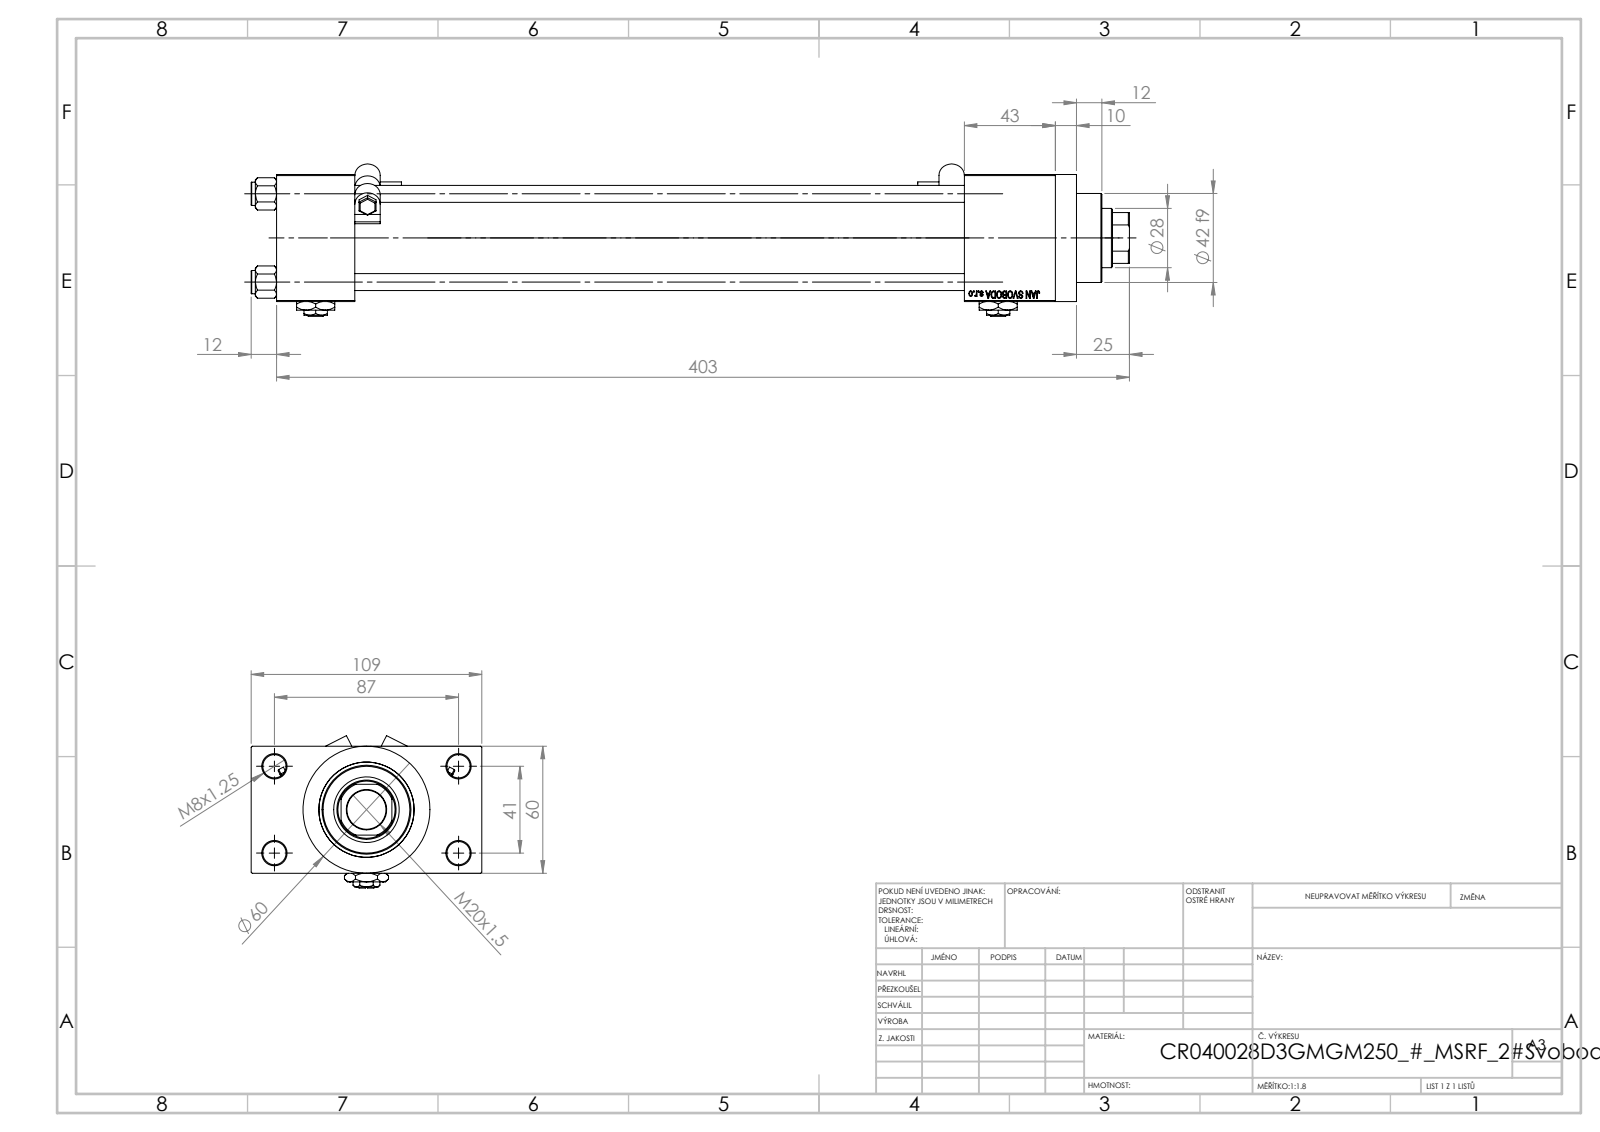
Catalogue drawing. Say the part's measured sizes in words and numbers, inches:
The part is named "V215CR_D_TYCINKA; NUT_M5_D; Zatka_pro_OIL_PORT; V215CR_VCP_D (+3 more)". Its 3-D file was written by "SolidWorks 2019 (CONFIG_CONTROL_DESIGN)". It is 15 solids with 1269 faces: 582 planar, 127 cylindrical and 560 other. Overall it measures 16.339 by 4.291 by 2.833 inches. Its volume is 49.74 cubic inches and its surface area 374.2 square inches. Round holes: 4 of diameter 0.315, 4 of diameter 0.433, 4 of diameter 0.656, 4 of diameter 0.945, 3 of diameter 0.276, 1 of diameter 0.728, 1 of diameter 1.102, 1 of diameter 1.22, 1 of diameter 1.575, 1 of diameter 1.772. Round bosses or shafts: 4 of diameter 0.433, 2 of diameter 0.197, 2 of diameter 0.098, 1 of diameter 2.362, 1 of diameter 1.811, 1 of diameter 1.654. Partial cylindrical surfaces (rounded edges, fillets, slot ends): 12 of radius 0.02, 4 of radius 0.236, 1 of radius 0.531. The main face-to-face distances are 2.362, 11.339, 0.965, 12.795, 3.327, 1.457, 14.488, 13.031, 1.693, 4.291. The hole center spacings are 0.892, 1.161, 1.642, 1.856, 1.893, 2.533, 3.011, 1.614.
